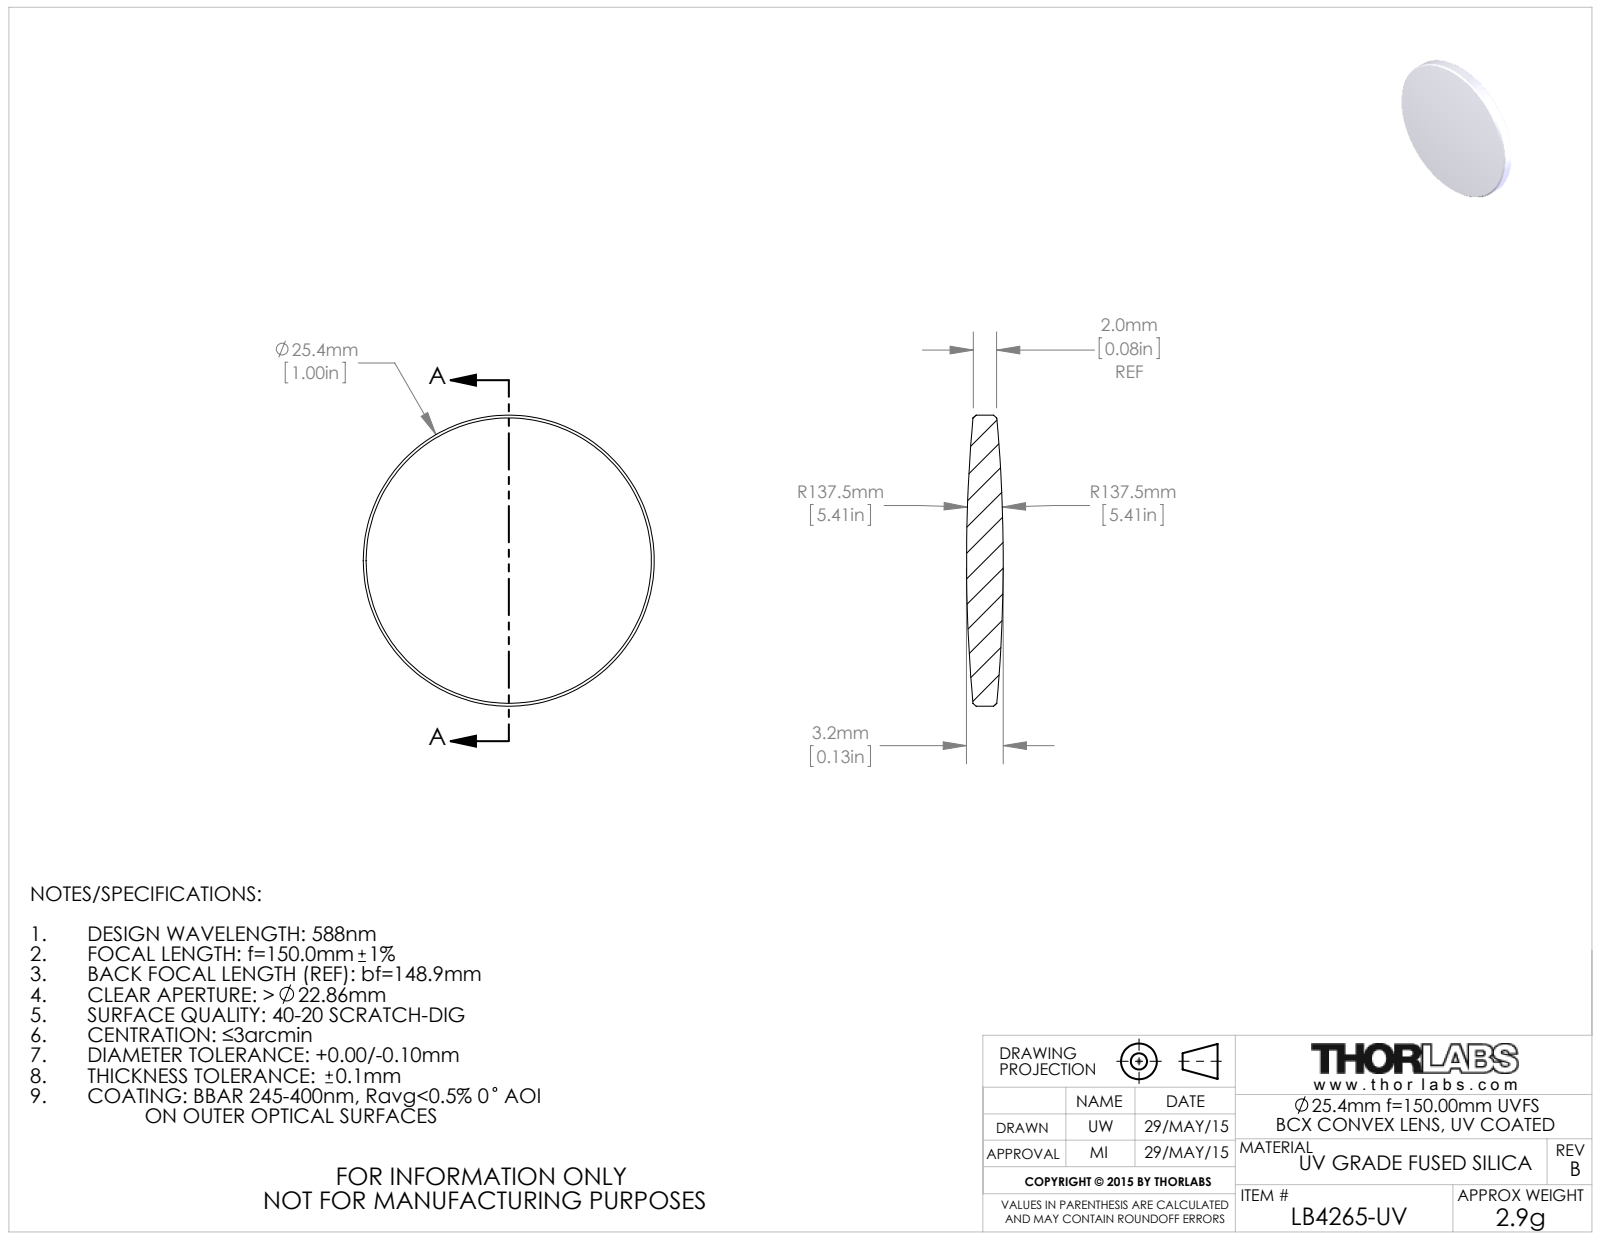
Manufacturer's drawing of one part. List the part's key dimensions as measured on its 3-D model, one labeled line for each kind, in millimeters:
Part name (STEP PRODUCT): 4323-E0W
STEP written by: SolidWorks 2014 (CONFIG_CONTROL_DESIGN)
Units: millimetres
Bodies: 1 solid, 10 faces (0 planar, 2 cylindrical, 8 other)
Overall size (bounding box): 25.4 × 25.4 × 3.2
Volume: 1 319 mm³ · Surface area: 1 156 mm²
Round bosses / shafts (diameter × count): ⌀25.4 ×1
